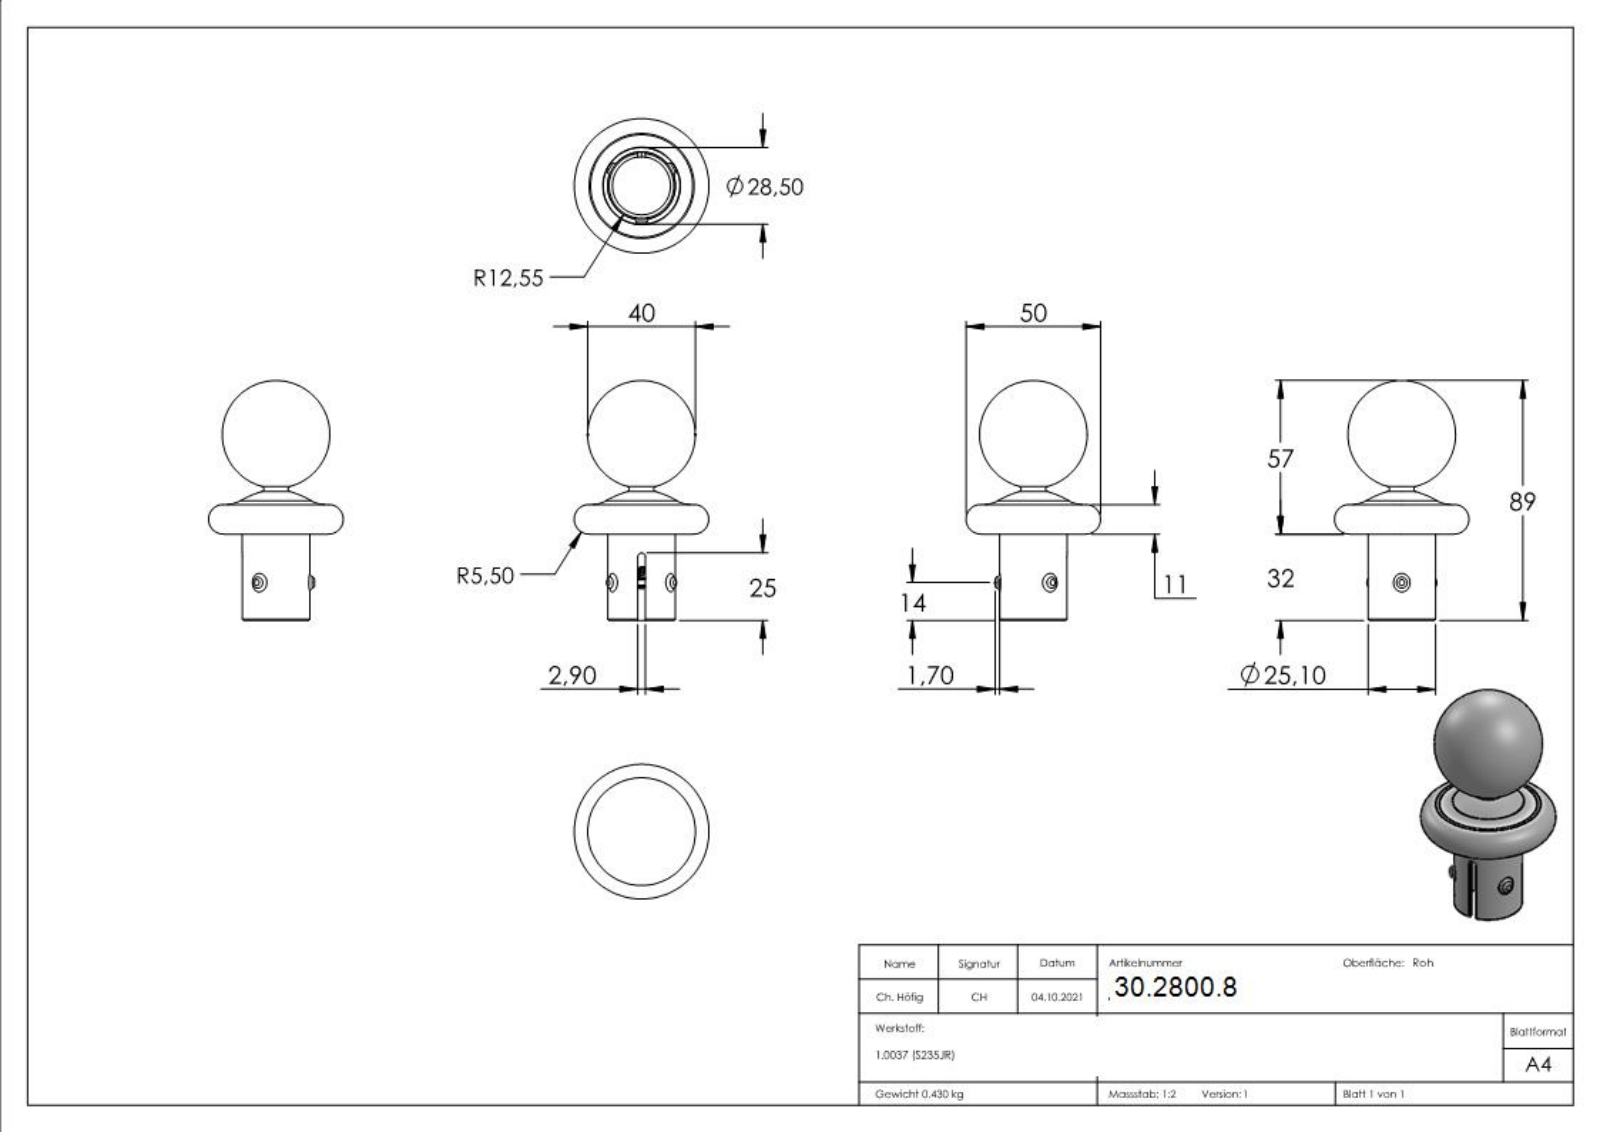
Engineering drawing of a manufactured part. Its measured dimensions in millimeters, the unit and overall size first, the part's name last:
Units: millimetres
Overall size (bounding box): 89 × 50 × 50
Round holes (diameter × count): ⌀21.5 ×1
Round bosses / shafts (diameter × count): ⌀25.1 ×1
Partial cylindrical surfaces — rounded edges, fillets, slot ends (radius × count): R1.45 ×1, R10.85 ×1
Main face-to-face distances: 8, 35, 43, 32, 3, 11, 2.9, 2.7, 2.02, 2.46
Volume: 55 142 mm³ · Surface area: 15 403 mm²
Bodies: 1 solid, 289 faces (120 planar, 31 cylindrical, 138 other)
Part name (STEP PRODUCT): 50259-ST
STEP written by: SolidWorks 2018 (CONFIG_CONTROL_DESIGN)
